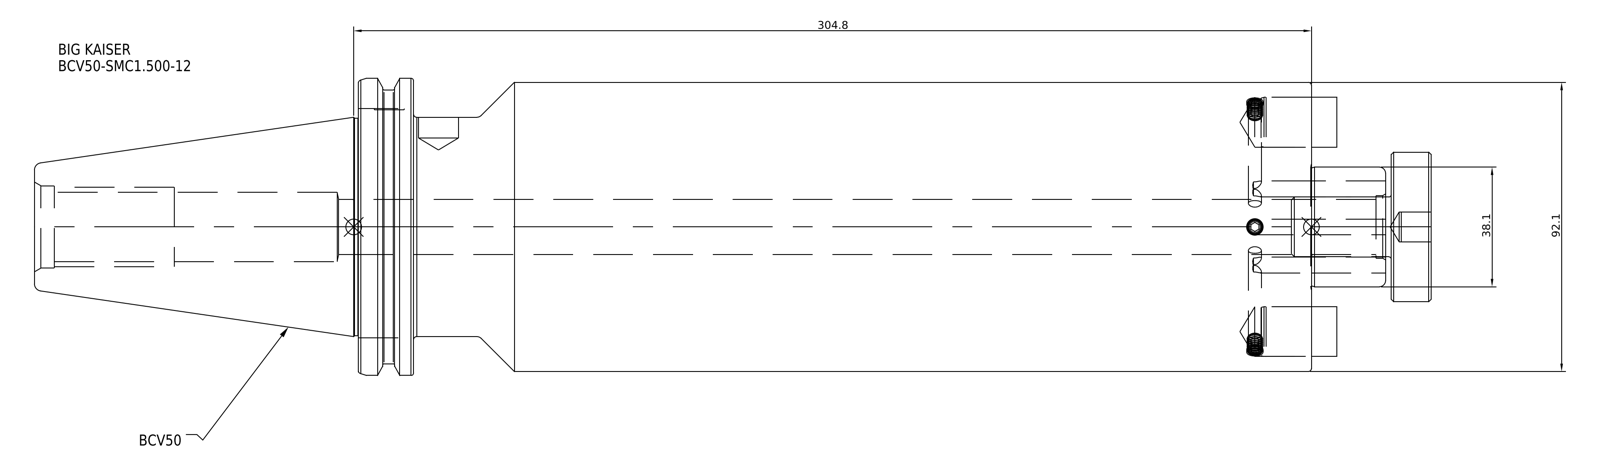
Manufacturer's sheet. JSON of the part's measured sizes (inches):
{"part_name": "BCV50-SMC1_500-12", "step_written_by": "SolidWorks 2021 (CONFIG_CONTROL_DESIGN)", "units": "inches", "bodies": {"solids": 1, "faces": 39, "planar": 17, "cylindrical": 14, "other": 8}, "overall_size": [16.318, 3.875, 3.875], "volume_in3": 131.1, "surface_area_in2": 214.1, "round_holes": [[0.687, 1]], "round_bosses_or_shafts": [[3.875, 1], [3.626, 1], [3.594, 1], [2.75, 1]], "face_to_face_distances": [11.941, 11.25, 0.691, 16, 4.75, 4.059, 0.625, 0.318, 11.568, 12.259]}
